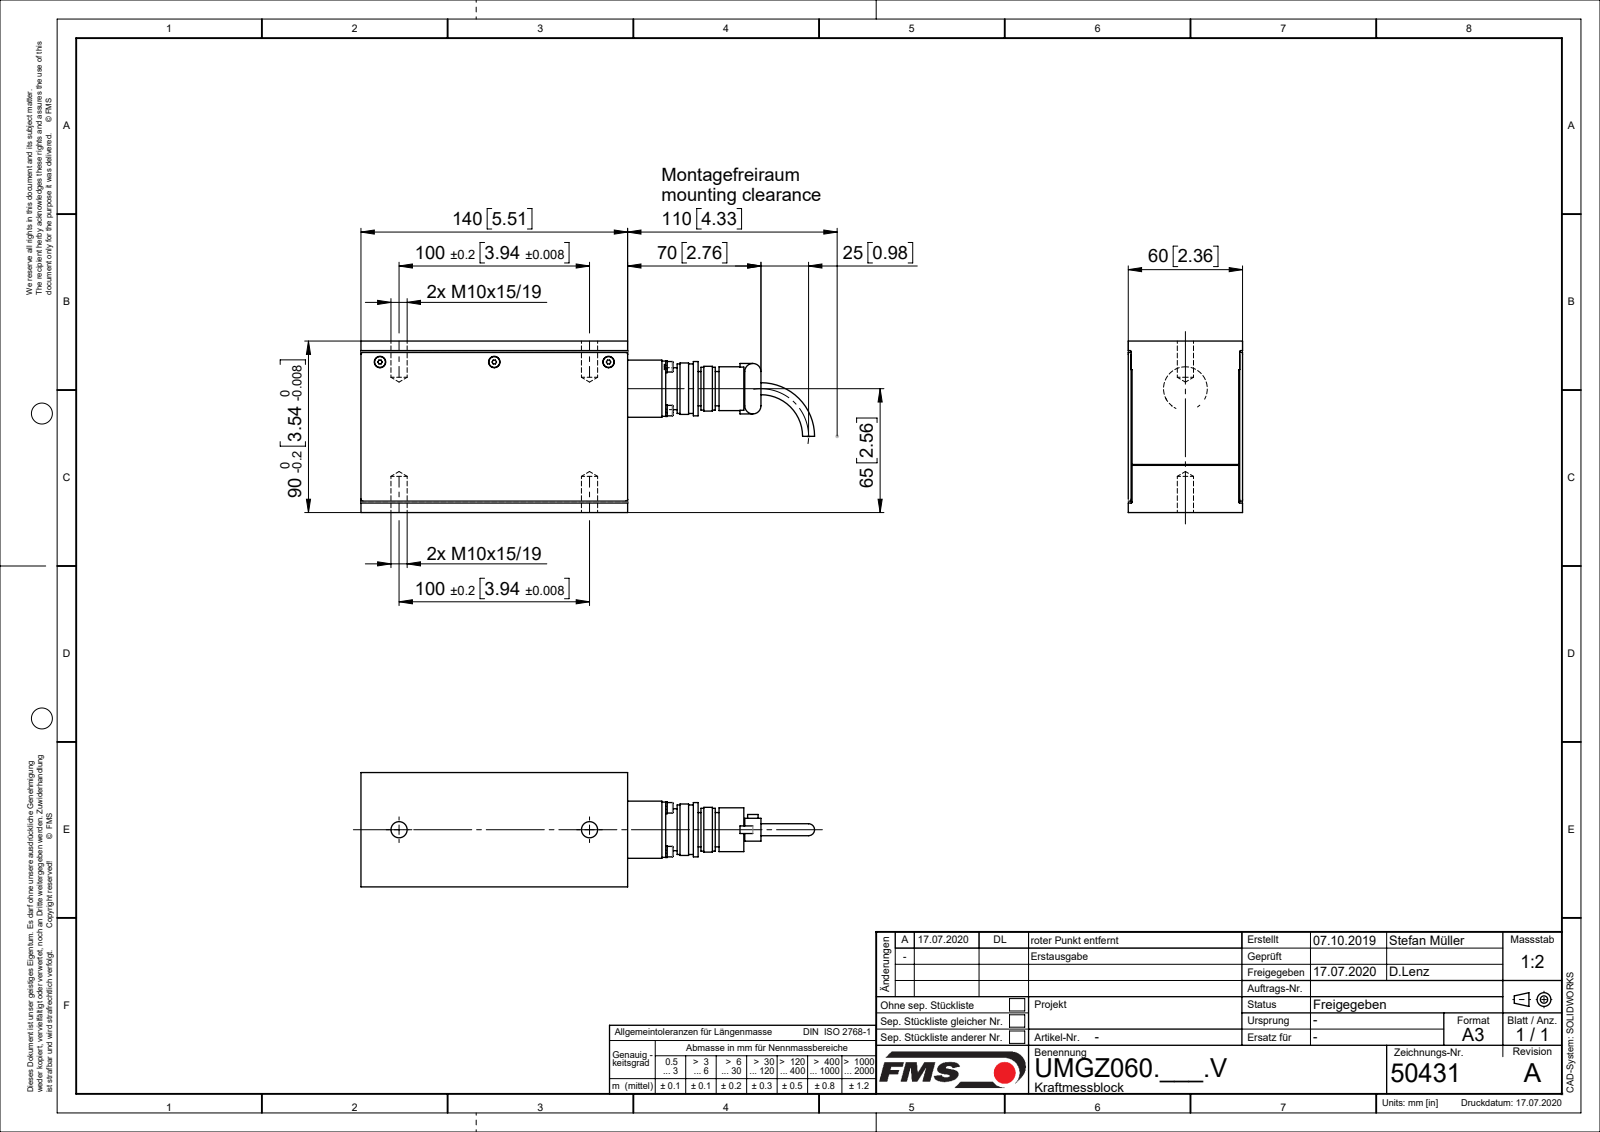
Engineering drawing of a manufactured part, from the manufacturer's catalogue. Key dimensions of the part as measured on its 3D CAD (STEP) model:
Part name (STEP PRODUCT): U50431; U5124404; U49515; KABELDOSE_PG_AMPH_4-POL (+4 more)
STEP written by: Mechanical Desktop 2009 (CONFIG_CONTROL_DESIGN)
Units: millimetres
Bodies: 18 solids, 384 faces (138 planar, 160 cylindrical, 86 other)
Overall size (bounding box): 243 × 90 × 60
Volume: 690 308 mm³ · Surface area: 118 214 mm²
Round holes (diameter × count): ⌀2.6 ×7, ⌀3.2 ×4, ⌀6 ×3, ⌀8.68 ×2, ⌀8.91 ×1
Round bosses / shafts (diameter × count): ⌀3 ×7, ⌀6.2 ×4, ⌀5.5 ×4, ⌀2.5 ×4, ⌀28 ×1, ⌀23 ×1, ⌀22 ×1, ⌀21 ×1
Partial cylindrical surfaces — rounded edges, fillets, slot ends (radius × count): R1 ×4, R4 ×4, R9 ×4
Main face-to-face distances: 1.5, 58.5, 57, 60, 48.5, 2, 10, 8.5, 50, 58
Hole centre spacings: 23, 32.53, 60, 100, 120
